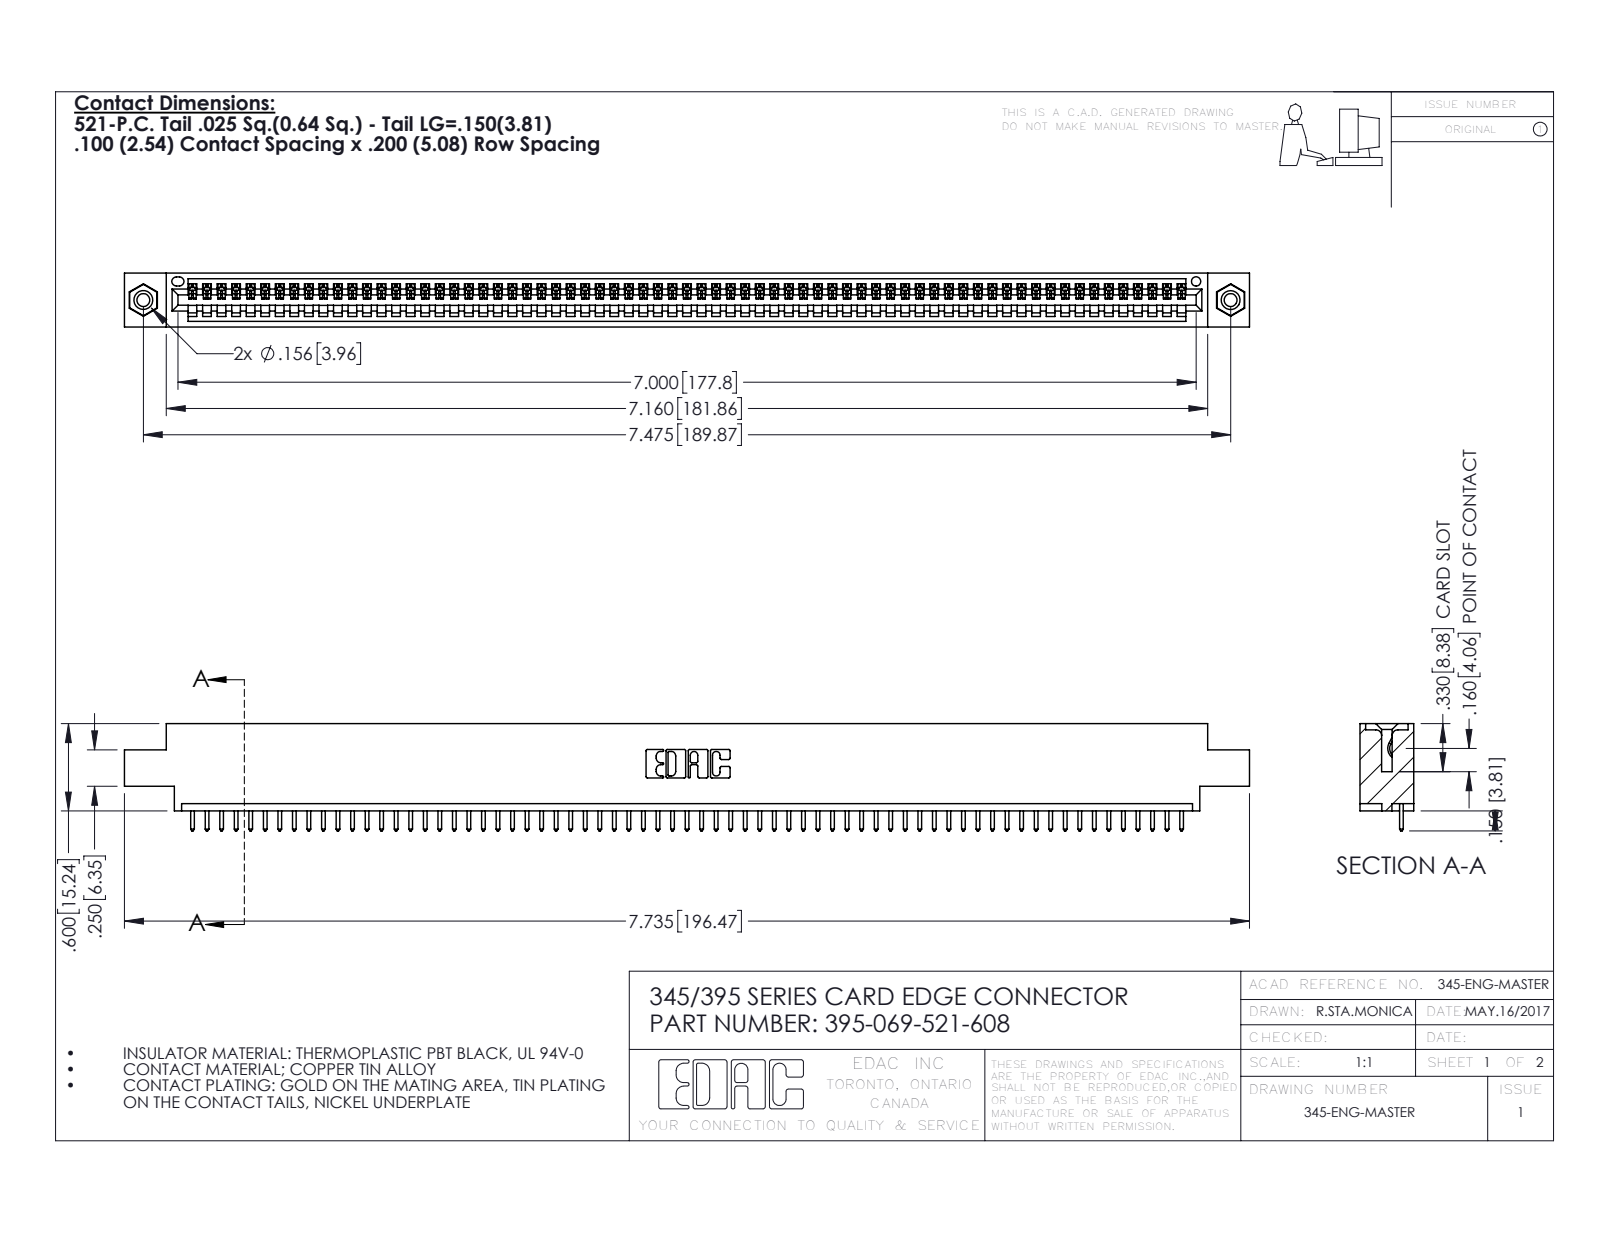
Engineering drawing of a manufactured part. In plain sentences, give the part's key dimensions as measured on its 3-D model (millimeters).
The part is named "395-069-521-608; 345 Part_0.170 Offset - 0.156 Dia-TI; 345-250-001_345-250-003-102; 345-292-001_345-293-121". Its 3-D file was written by "SolidWorks 2016 (CONFIG_CONTROL_DESIGN)". It is 72 solids with 4192 faces: 2876 planar, 1300 cylindrical and 16 other. Overall it measures 196.5 by 18.7 by 9.4 millimeters. Its volume is 18 570 cubic millimeters and its surface area 24 420 square millimeters. Round holes: 2 of diameter 2.3, 2 of diameter 3.2, 2 of diameter 4, 1 of diameter 1.6. Round bosses or shafts: 2 of diameter 3.9. Partial cylindrical surfaces (rounded edges, fillets, slot ends): 138 of radius 0.2, 138 of radius 0.3, 22 of radius 0.3, 6 of radius 0.2, 6 of radius 0.8, 3 of radius 0.7, 2 of radius 0.8, 2 of radius 1. The main face-to-face distances are 1.8, 7.6, 9.4, 5.1, 2.5, 6.9, 0.6, 5.7, 4.4, 3.8. The hole center spacings are 6.9, 183.9, 189.9.
